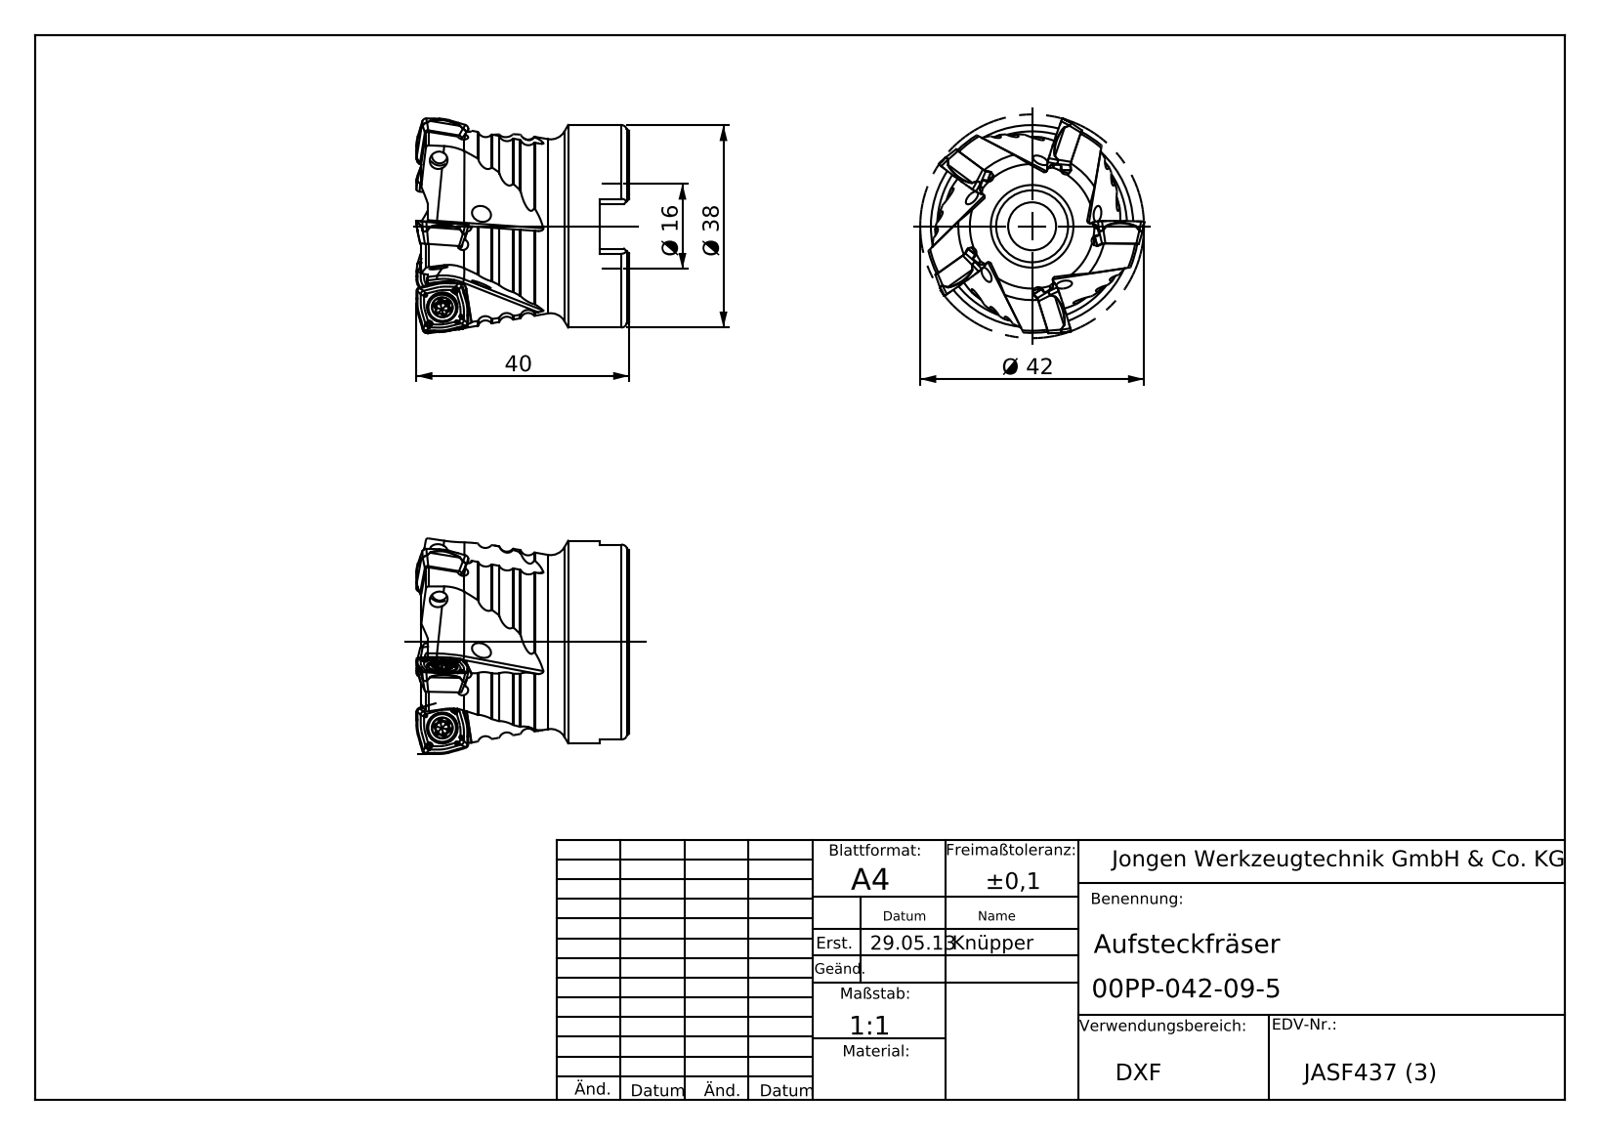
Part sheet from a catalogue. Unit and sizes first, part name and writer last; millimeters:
Units: millimetres
Overall size (bounding box): 42.03 × 42.03 × 39.93
Round holes (diameter × count): ⌀3 ×5, ⌀9 ×1, ⌀13.5 ×1, ⌀15.85 ×1, ⌀16.15 ×1, ⌀16.3 ×1
Round bosses / shafts (diameter × count): ⌀38 ×1
Partial cylindrical surfaces — rounded edges, fillets, slot ends (radius × count): R0.5 ×10, R0.8 ×10, R1 ×5, R2 ×5
Main face-to-face distances: 37.75, 5.6, 32.15, 8.4, 27, 21.4, 10.75, 20, 14.4, 7
Volume: 33 026 mm³ · Surface area: 10 245 mm²
Bodies: 1 solid, 196 faces (54 planar, 41 cylindrical, 101 other)
Part name (STEP PRODUCT): 00PP-042-09-5
STEP written by: SolidWorks 2013 (AUTOMOTIVE_DESIGN)
